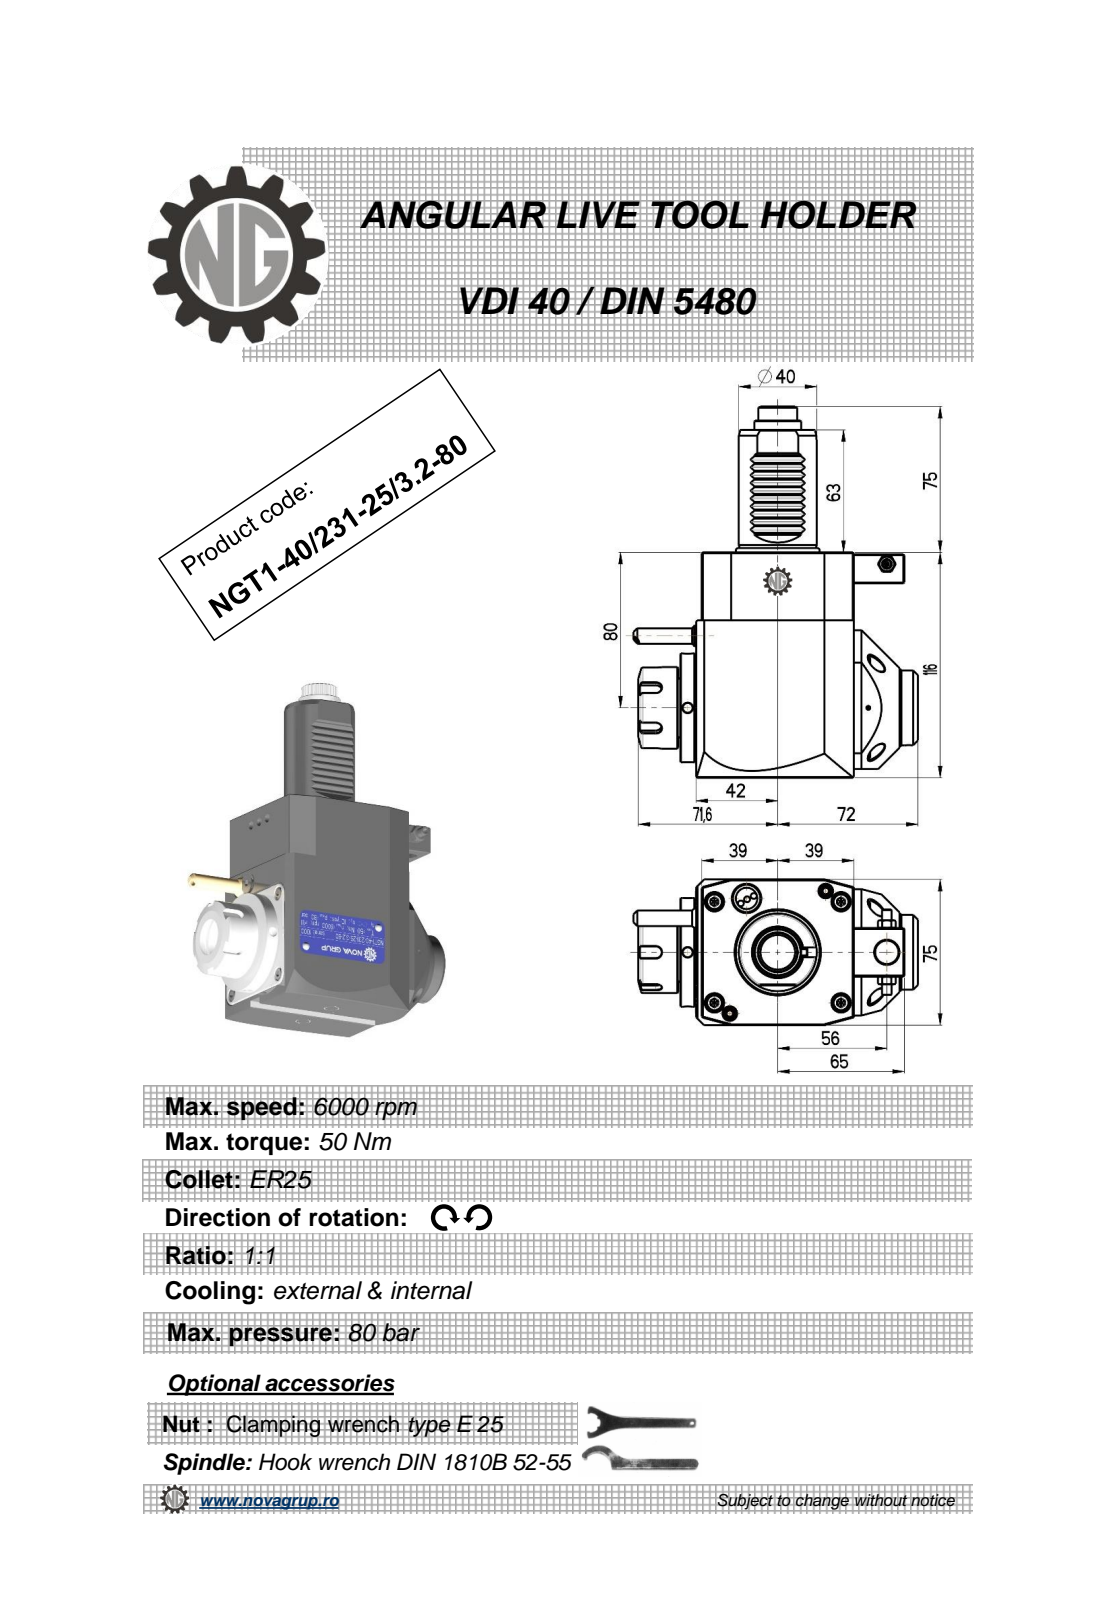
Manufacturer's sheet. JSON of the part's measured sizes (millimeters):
{"part_name": "NGT1_40_231_25_3_2_80", "step_written_by": "PRO/ENGINEER BY PARAMETRIC TECHNOLOGY CORPORATION, 2010280 (CONFIG_CONTROL_DESIGN)", "units": "millimeters", "bodies": {"solids": 1, "faces": 549, "planar": 193, "cylindrical": 183, "other": 173}, "overall_size": [191, 146.14, 75], "volume_mm3": 897258, "surface_area_mm2": 72176, "round_holes": [[5, 3], [3, 1], [4.2, 1], [9.5, 1], [12, 1], [20.3, 1]], "round_bosses_or_shafts": [[56, 1], [43, 1], [42, 1], [40, 1], [38.5, 1], [33, 1], [24, 1], [11.2, 1]], "partial_cylinders_radius": [[2.08, 48], [0.26, 12], [0.3, 10], [0.22, 6], [3, 5], [9.08, 1], [9.92, 1], [15, 1]], "face_to_face_distances": [75, 116, 81, 78, 3, 11, 8, 7.5, 2.8, 80.8], "hole_center_spacings": [38.68, 40.93, 71.5, 102.25, 126.22]}
